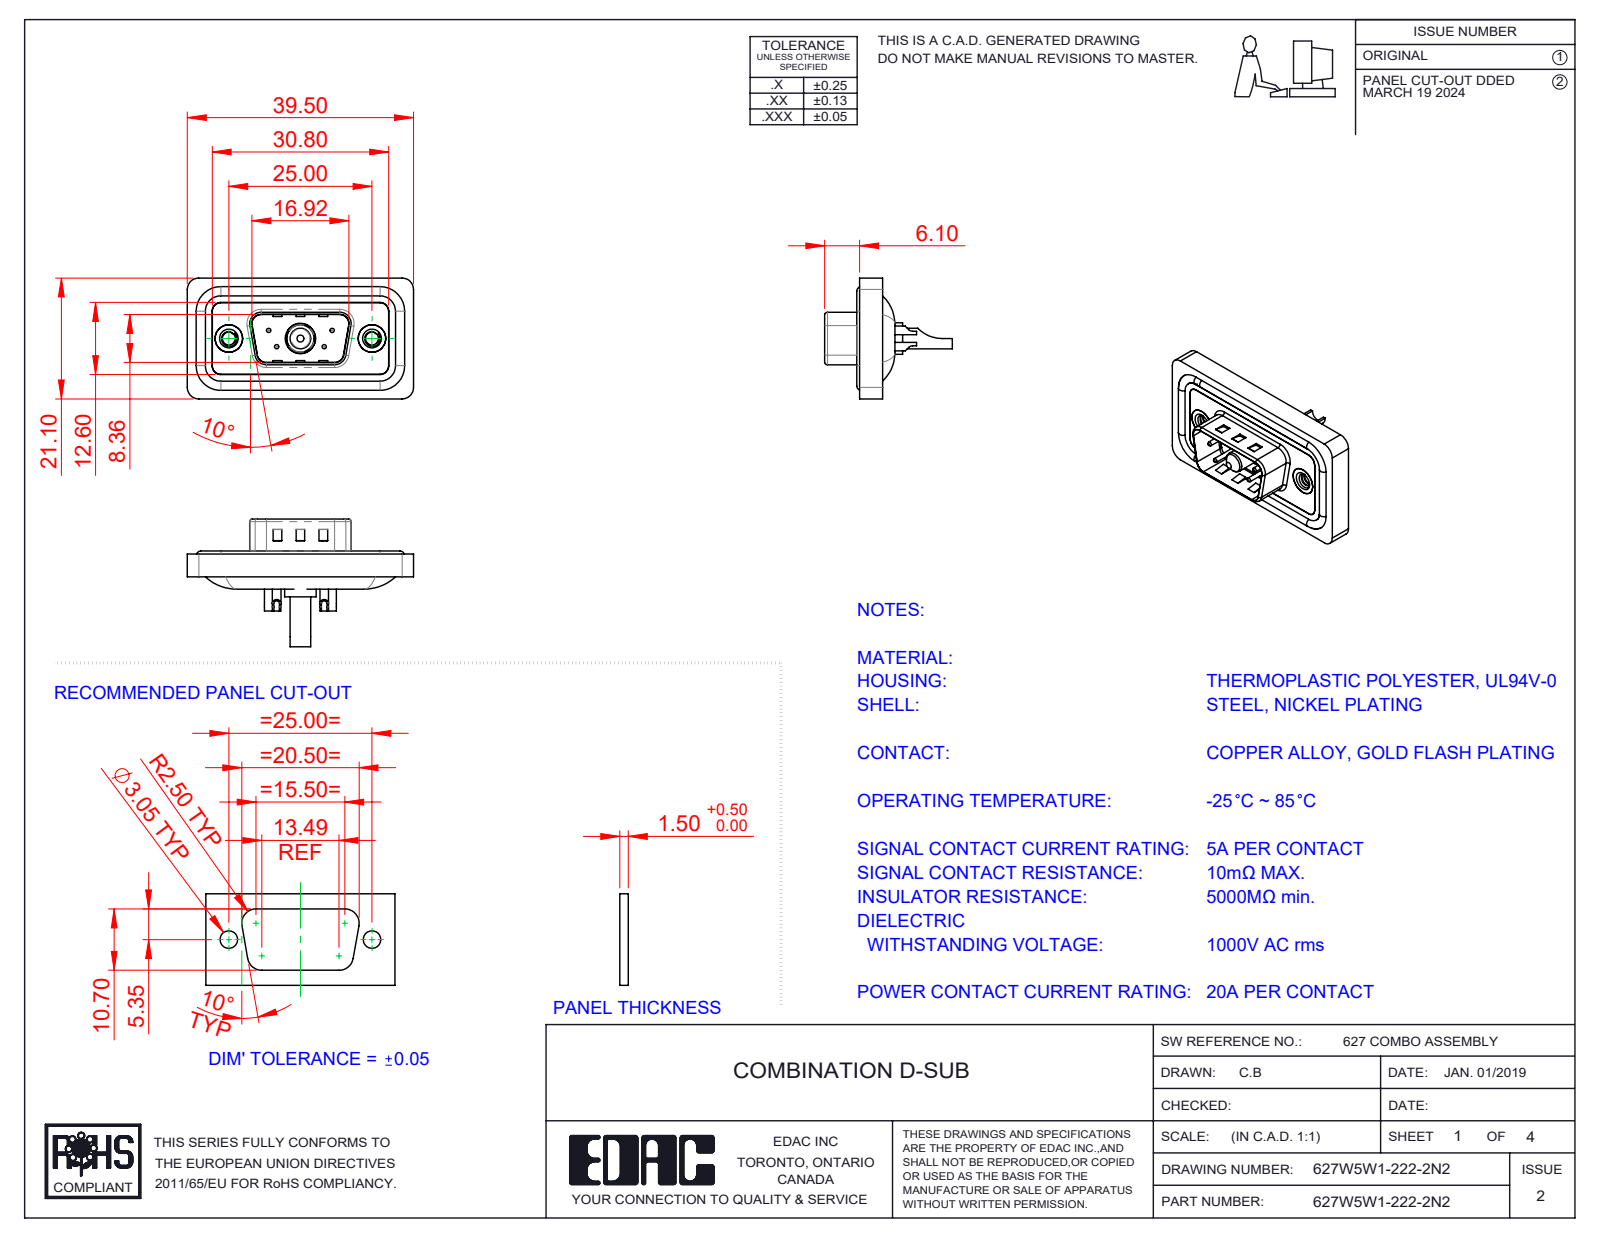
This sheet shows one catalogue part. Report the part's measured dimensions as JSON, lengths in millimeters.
{"part_name": "627Combo Threaded Rivet_2; 627W5W1-222-2N2; 627Combo Waterproof Housing_09 Contacts; 627Combo Housing_5W1 (+5 more)", "step_written_by": "SolidWorks 2023 (CONFIG_CONTROL_DESIGN)", "units": "millimeters", "bodies": {"solids": 13, "faces": 605, "planar": 194, "cylindrical": 266, "other": 145}, "overall_size": [39.5, 22.3, 21.1], "volume_mm3": 4406, "surface_area_mm2": 7056, "round_holes": [[0.75, 4], [1, 4], [1.6, 4], [2, 4], [2.26, 2], [4, 2], [4.8, 2], [5, 2], [2.7, 1], [4.85, 1], [5.3, 1]], "round_bosses_or_shafts": [[1.6, 4], [1.5, 4], [4.9, 2], [5.5, 1], [5.2, 1], [4.75, 1], [3.75, 1], [3.6, 1]], "partial_cylinders_radius": [[1.5, 22], [2, 18], [0.5, 8], [1.6, 8], [1, 6], [0.25, 4], [0.6, 4], [0.65, 4]], "face_to_face_distances": [0.4, 1.1, 2.9, 1.6, 3.1, 0.5, 1.5, 2.5, 4, 0.8], "hole_center_spacings": [3.16, 5.72, 7.1, 12.5, 18.1, 4.39, 4.4, 8.31]}
